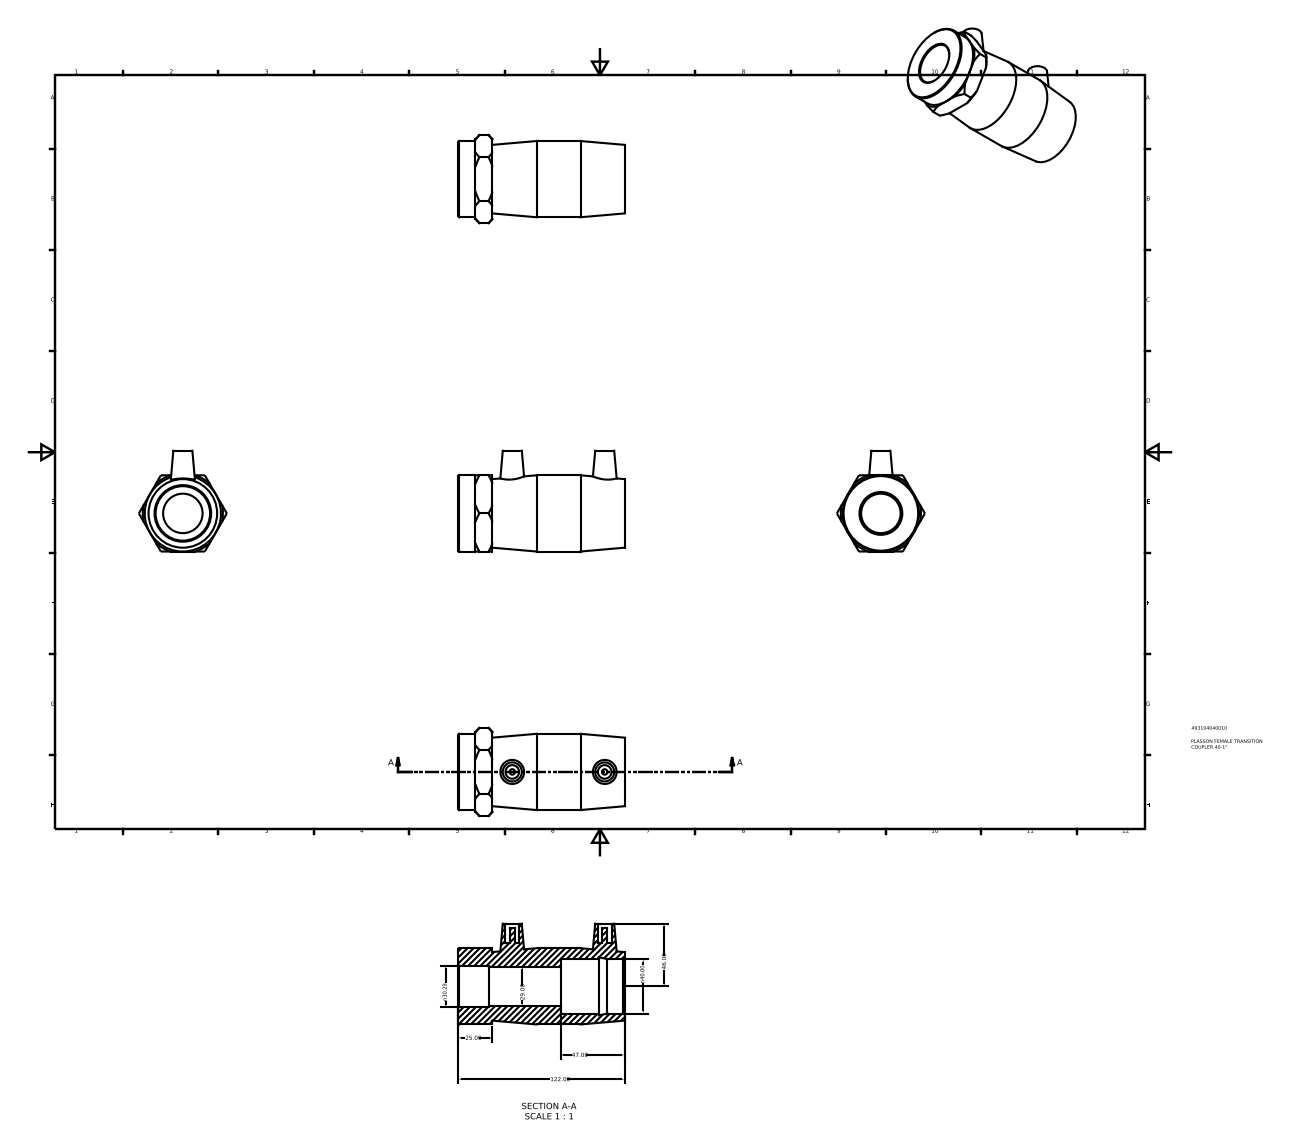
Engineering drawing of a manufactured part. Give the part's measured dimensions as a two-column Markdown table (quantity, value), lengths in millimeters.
| quantity | value |
| --- | --- |
| part name | 493104040010 |
| STEP written by | Autodesk Inventor 2015 (AUTOMOTIVE_DESIGN) |
| units | millimeters |
| bodies | 1 solid, 54 faces (24 planar, 10 cylindrical, 20 other) |
| overall size | 122 × 74 × 64.66 |
| volume | 183 350 mm³ |
| surface area | 41 011 mm² |
| round holes (diameter × count) | 10 × 2, 29 × 1, 30.29 × 1, 40 × 1 |
| round bosses / shafts (diameter × count) | 4 × 2, 56 × 1 |
| main face-to-face distances | 56, 122, 25, 97, 75, 50, 47, 12.5, 103.2, 78.2 |
| hole center spacings | 67.9 |
